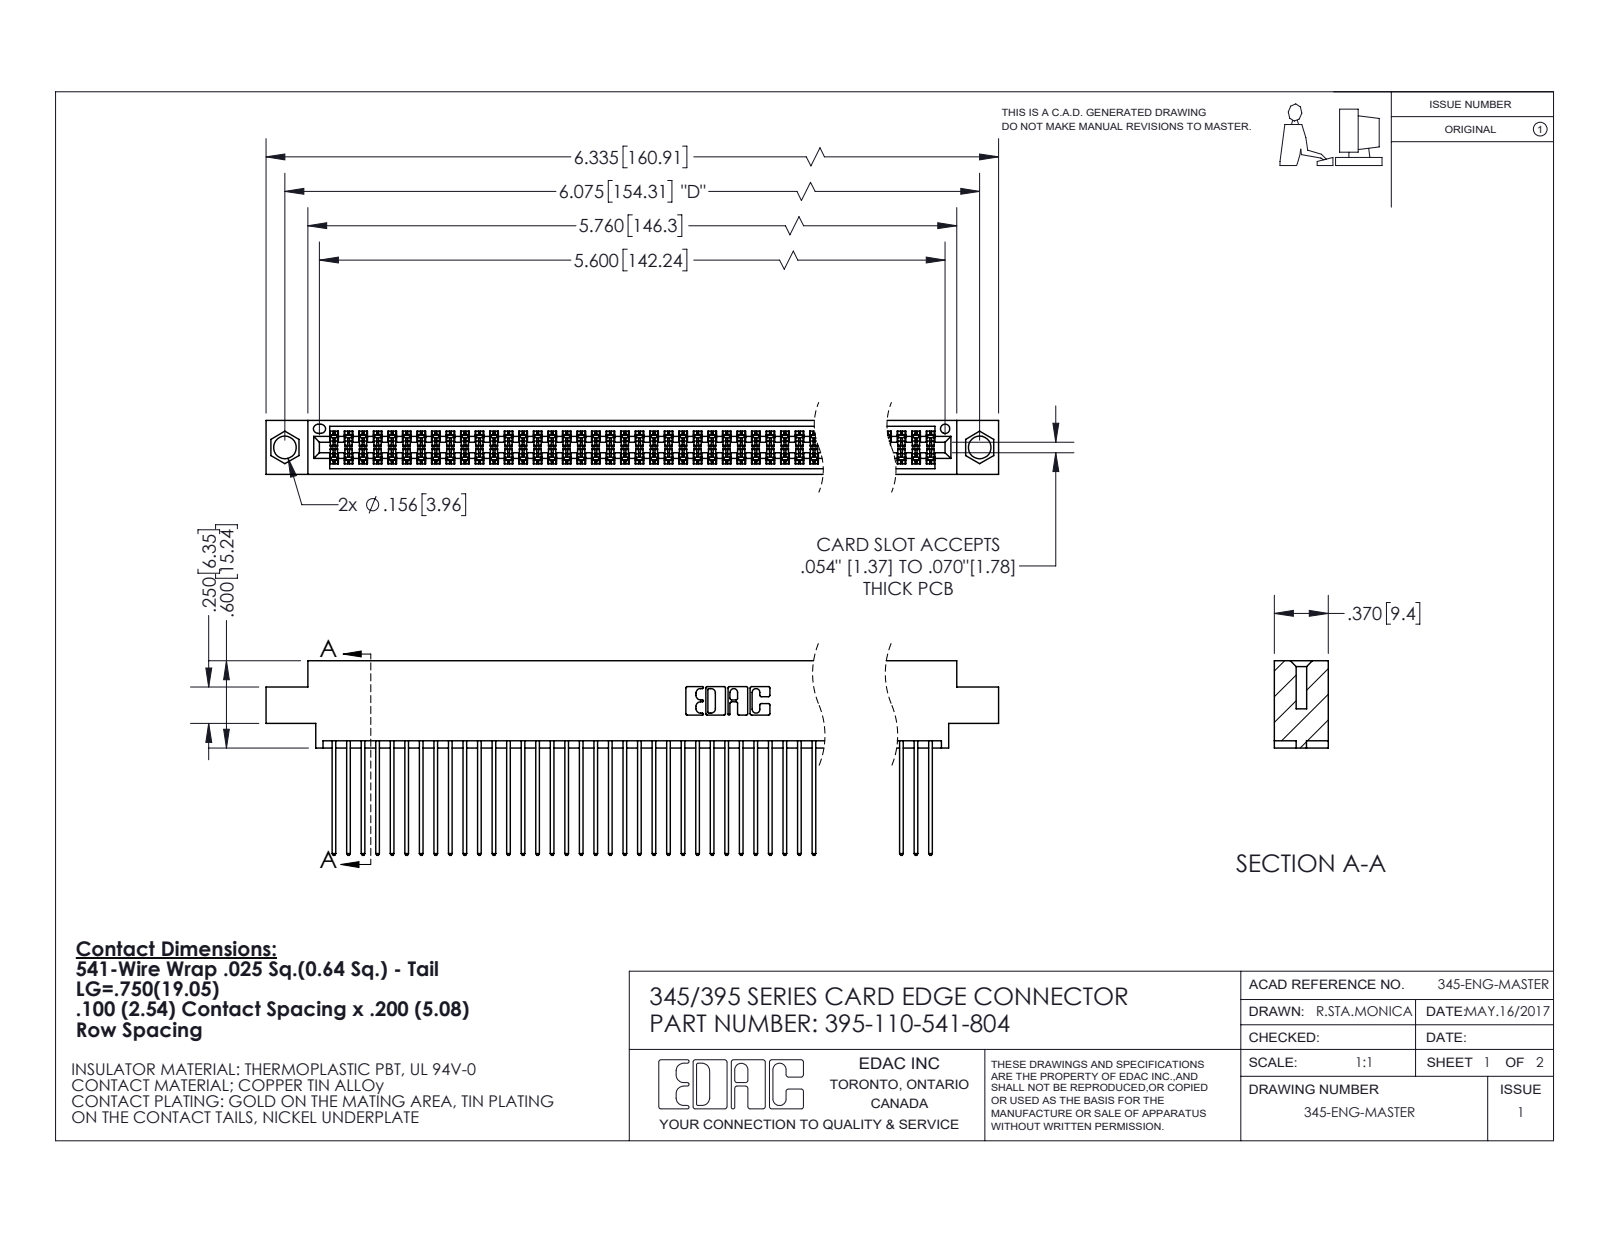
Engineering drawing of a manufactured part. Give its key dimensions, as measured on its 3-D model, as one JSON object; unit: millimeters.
{"part_name": "395-110-541-804; 345-292-001_345-293-141; 345 Part_0.170 Offset - 0.156 Dia-TI", "step_written_by": "SolidWorks 2020 (CONFIG_CONTROL_DESIGN)", "units": "millimeters", "bodies": {"solids": 111, "faces": 5644, "planar": 3728, "cylindrical": 1916, "other": 0}, "overall_size": [160.9, 34, 9.4], "volume_mm3": 16200, "surface_area_mm2": 27100, "round_holes": [[4, 2], [1.6, 1]], "partial_cylinders_radius": [[0.2, 220], [0.3, 110], [0.3, 22], [0.2, 6], [0.8, 6], [0.7, 3], [0.4, 2], [0.5, 2]], "face_to_face_distances": [1.8, 7.6, 5.1, 2.5, 6.9, 0.6, 5.7, 9.4, 4.4, 3.8], "hole_center_spacings": [6.9, 148.3, 154.3]}
